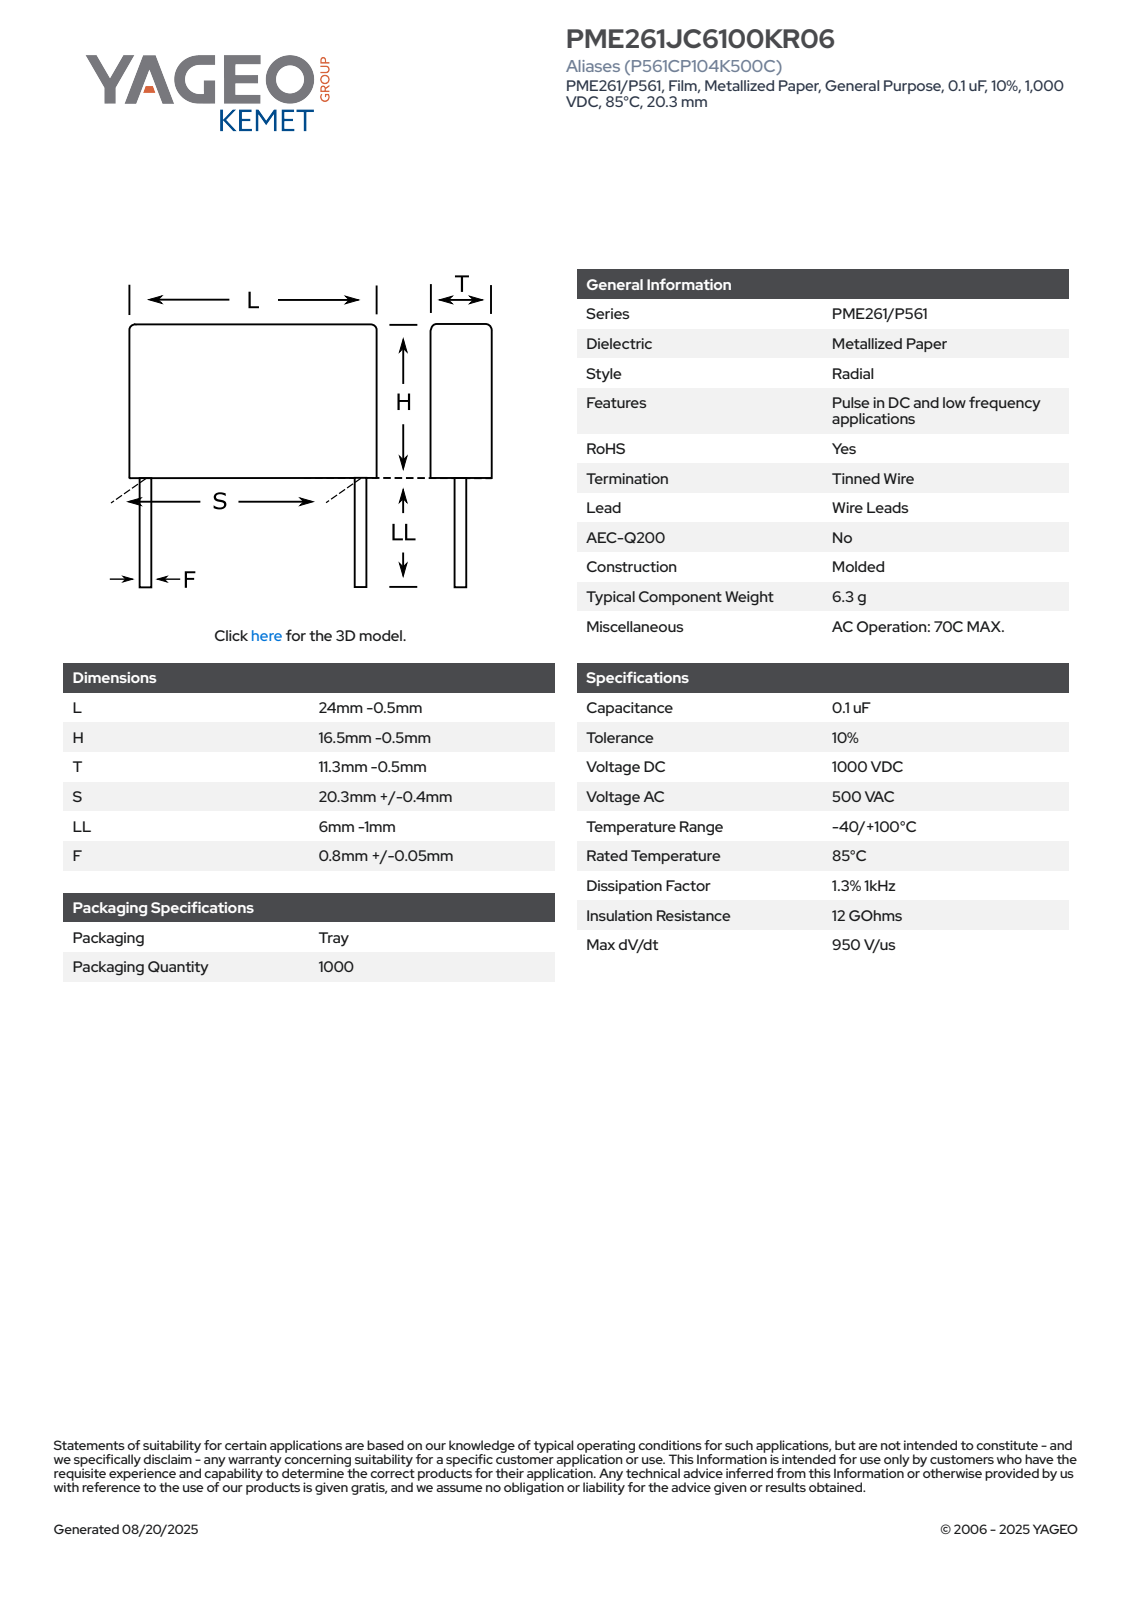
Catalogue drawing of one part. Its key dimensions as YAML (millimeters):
part_name: "CFR_MOLDED_24X16.5X11.3_L23.5H16T10.8S20.3LL5F0.85"
step_written_by: "SolidWorks 2014 (AUTOMOTIVE_DESIGN)"
units: millimeters
bodies: {solids: 4, faces: 73, planar: 65, cylindrical: 8, other: 0}
overall_size: [23.5, 21, 10.8]
volume: 4063
surface_area: 1644
round_bosses_or_shafts:
  - {diameter: 0.85, count: 2}
partial_cylinders:
  - {radius: 0.5, count: 4}
face_to_face_distances: [10.8, 16, 23.5, 5, 21, 13.81, 8.81, 7.19, 11.71, 6.71]
